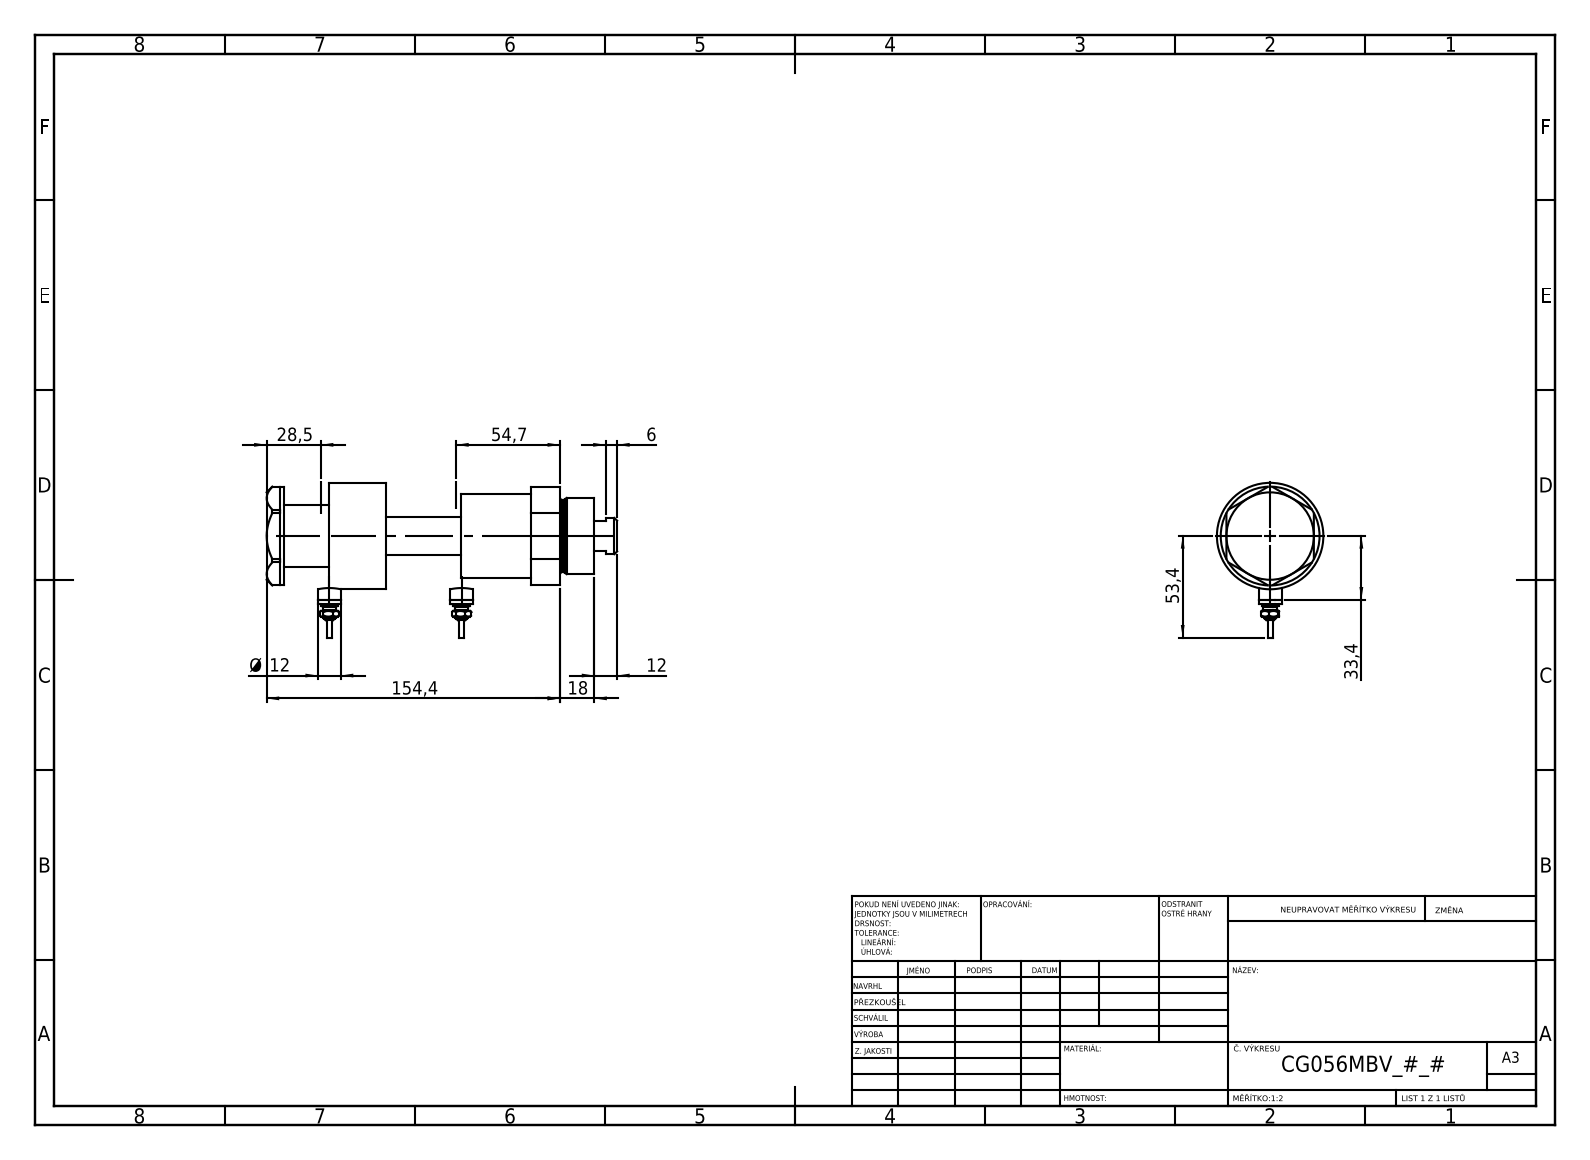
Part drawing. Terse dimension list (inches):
name: V270CG_MIDDLE; Switch; V270CG_BACK; V270CG_VC (+1 more)
written by: SolidWorks 2019 (CONFIG_CONTROL_DESIGN)
unit: in
bodies: 7 solids, 196 faces (79 planar, 53 cylindrical, 64 other)
size: 7.26 × 3.205 × 2.205
volume: 14.48 in³; area: 71.32 in²
holes: 1× ⌀0.256, 1× ⌀0.787, 1× ⌀0.846, 1× ⌀2.205
bosses: 2× ⌀0.472, 2× ⌀0.354, 2× ⌀0.276, 2× ⌀0.177, 2× ⌀0.098, 1× ⌀2.047, 1× ⌀1.732, 1× ⌀1.575
face distances: 1.171, 1.291, 2.463, 0.354, 0.937, 2.108, 4.035, 3.681, 2.744, 1.573
